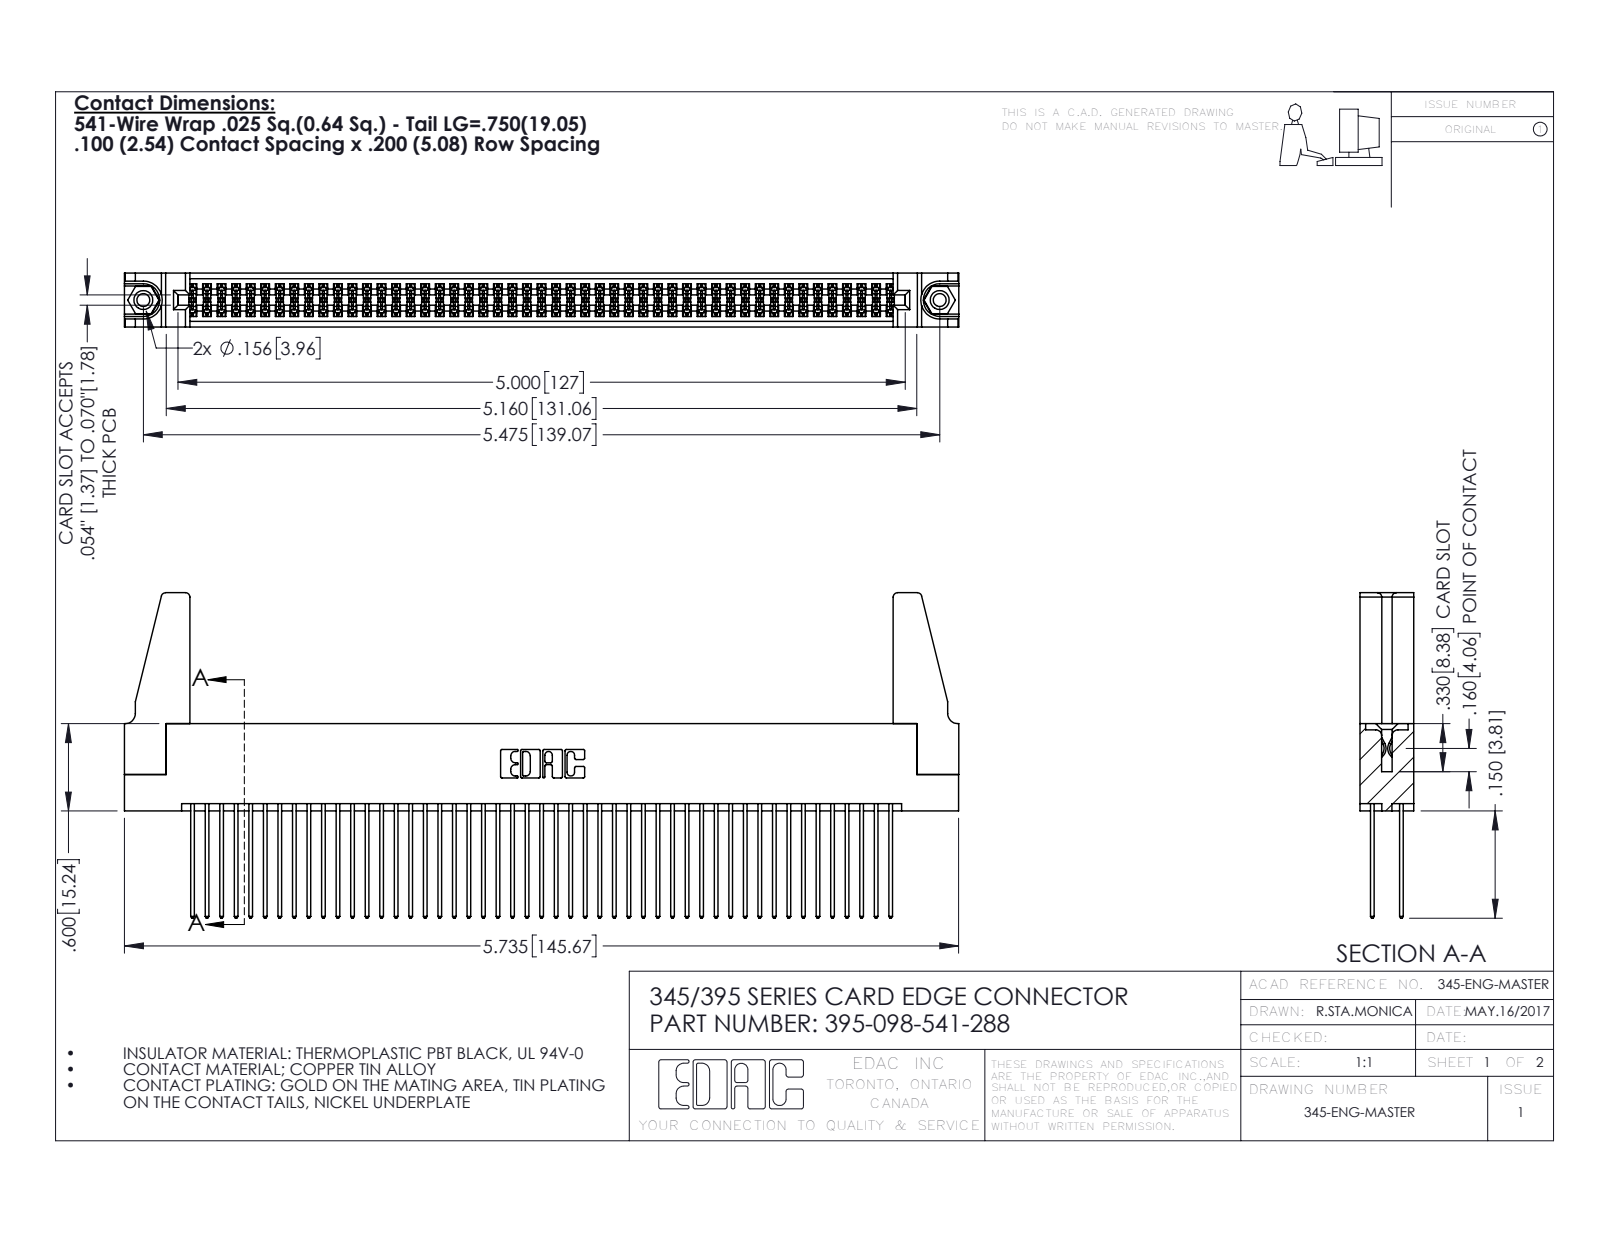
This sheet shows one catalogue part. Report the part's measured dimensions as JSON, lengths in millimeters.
{"part_name": "345-220-078_345-220-088; 345 Part_Flush Mounting Lugs - 0.156 Dia-TH; 395-098-541-288; 345-250-001_345-250-001-102 (+1 more)", "step_written_by": "SolidWorks 2016 (CONFIG_CONTROL_DESIGN)", "units": "millimeters", "bodies": {"solids": 103, "faces": 5150, "planar": 3386, "cylindrical": 1748, "other": 16}, "overall_size": [145.7, 56.8, 9.4], "volume_mm3": 18030, "surface_area_mm2": 27750, "round_holes": [[2.3, 2], [3.2, 2], [4, 2], [1.6, 1]], "round_bosses_or_shafts": [[3.9, 2]], "partial_cylinders_radius": [[0.2, 147], [0.3, 98], [0.3, 22], [0.8, 8], [0.2, 6], [0.8, 6], [0.7, 3], [0.4, 2]], "face_to_face_distances": [1.8, 7.6, 5.1, 2.5, 6.9, 0.6, 9.4, 5.7, 4.4, 3.8], "hole_center_spacings": [6.9, 133.1, 139.1]}
